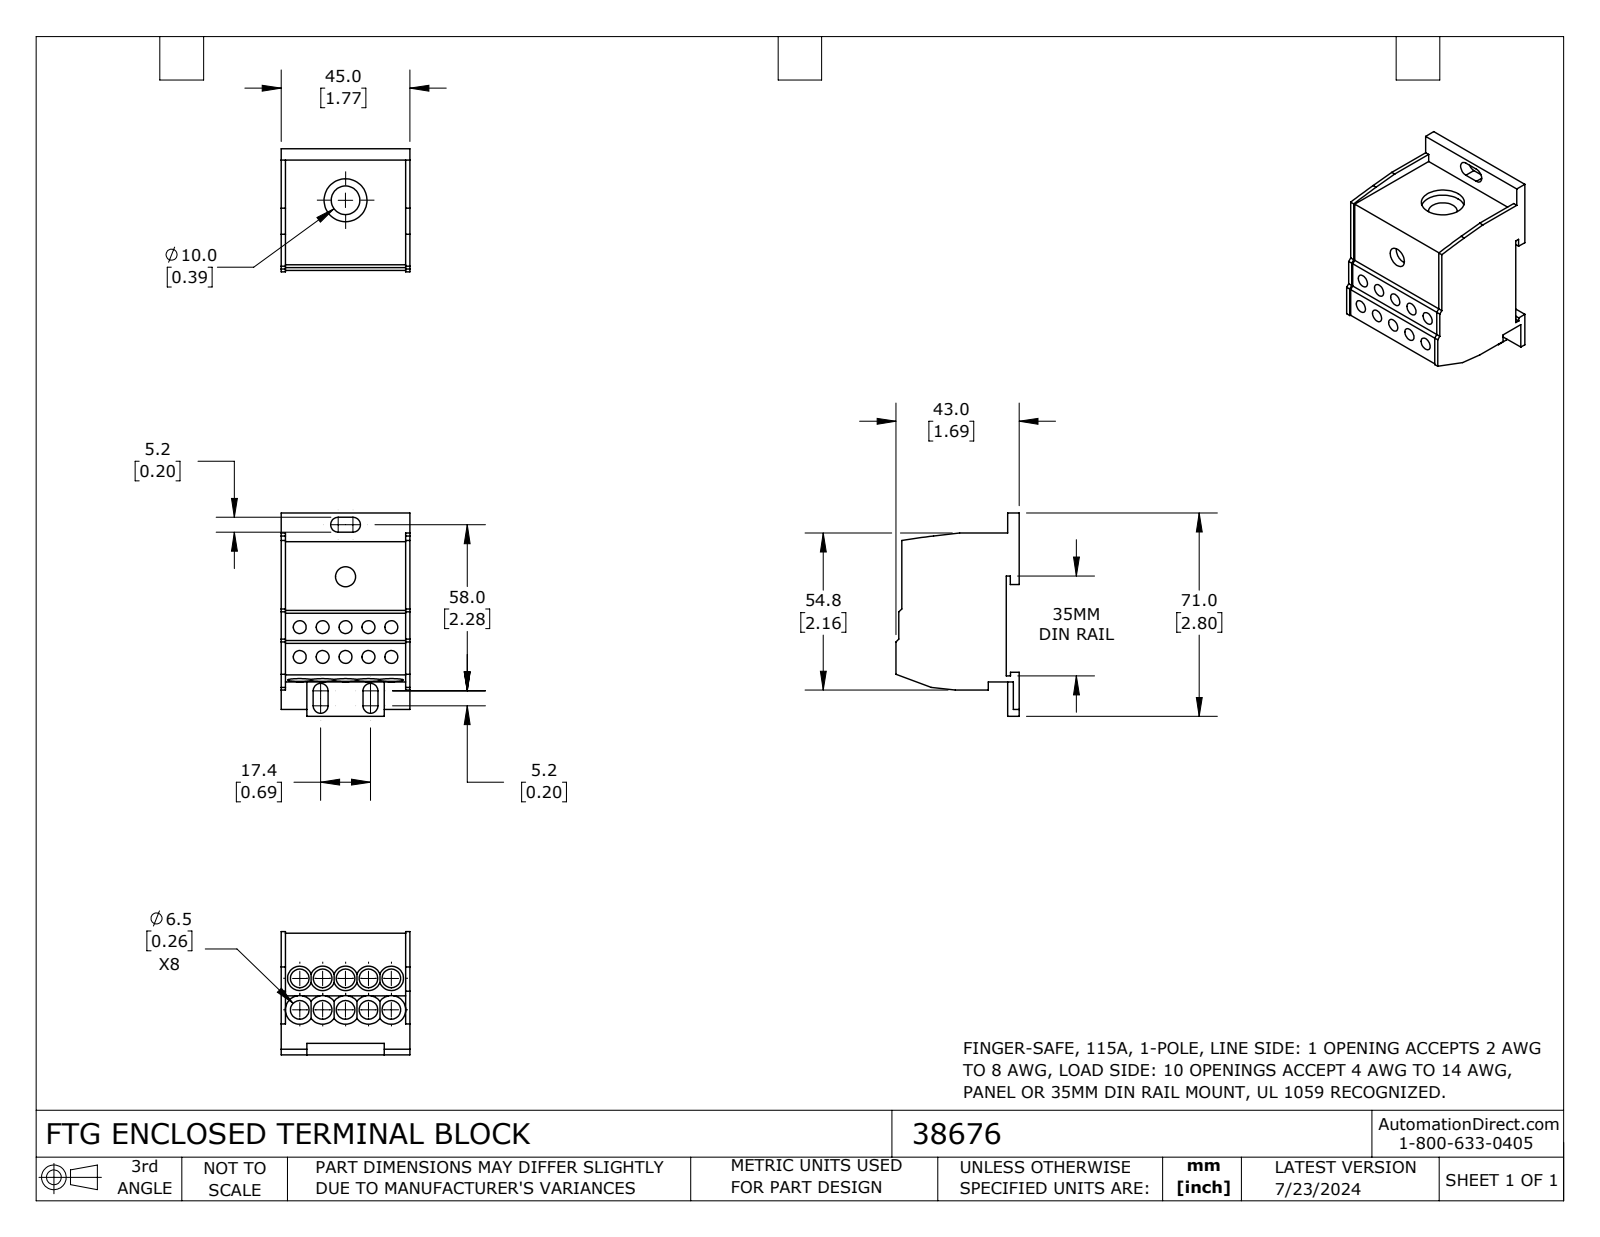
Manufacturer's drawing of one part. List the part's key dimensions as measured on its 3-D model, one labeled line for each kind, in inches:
Part name (STEP PRODUCT): 38676
STEP written by: SolidWorks 2023 (CONFIG_CONTROL_DESIGN)
Units: inches
Bodies: 1 solid, 235 faces (99 planar, 92 cylindrical, 44 other)
Overall size (bounding box): 2.795 × 1.772 × 1.693
Volume: 4.468 in³ · Surface area: 31.93 in²
Round holes (diameter × count): ⌀0.177 ×10, ⌀0.256 ×10, ⌀0.394 ×3, ⌀0.335 ×2, ⌀0.276 ×1, ⌀0.591 ×1
Partial cylindrical surfaces — rounded edges, fillets, slot ends (radius × count): R0.102 ×6, R0.187 ×4, R0.167 ×3, R0.197 ×3, R8.137 ×1
Main face-to-face distances: 1.772, 0.177, 1.594, 1.417, 0.02, 0.157, 0.079, 0.039, 1.437, 0.059
Hole centre spacings: 0.315, 0.63, 0.517, 0.535, 0.945, 0.751, 0.765, 0.409
